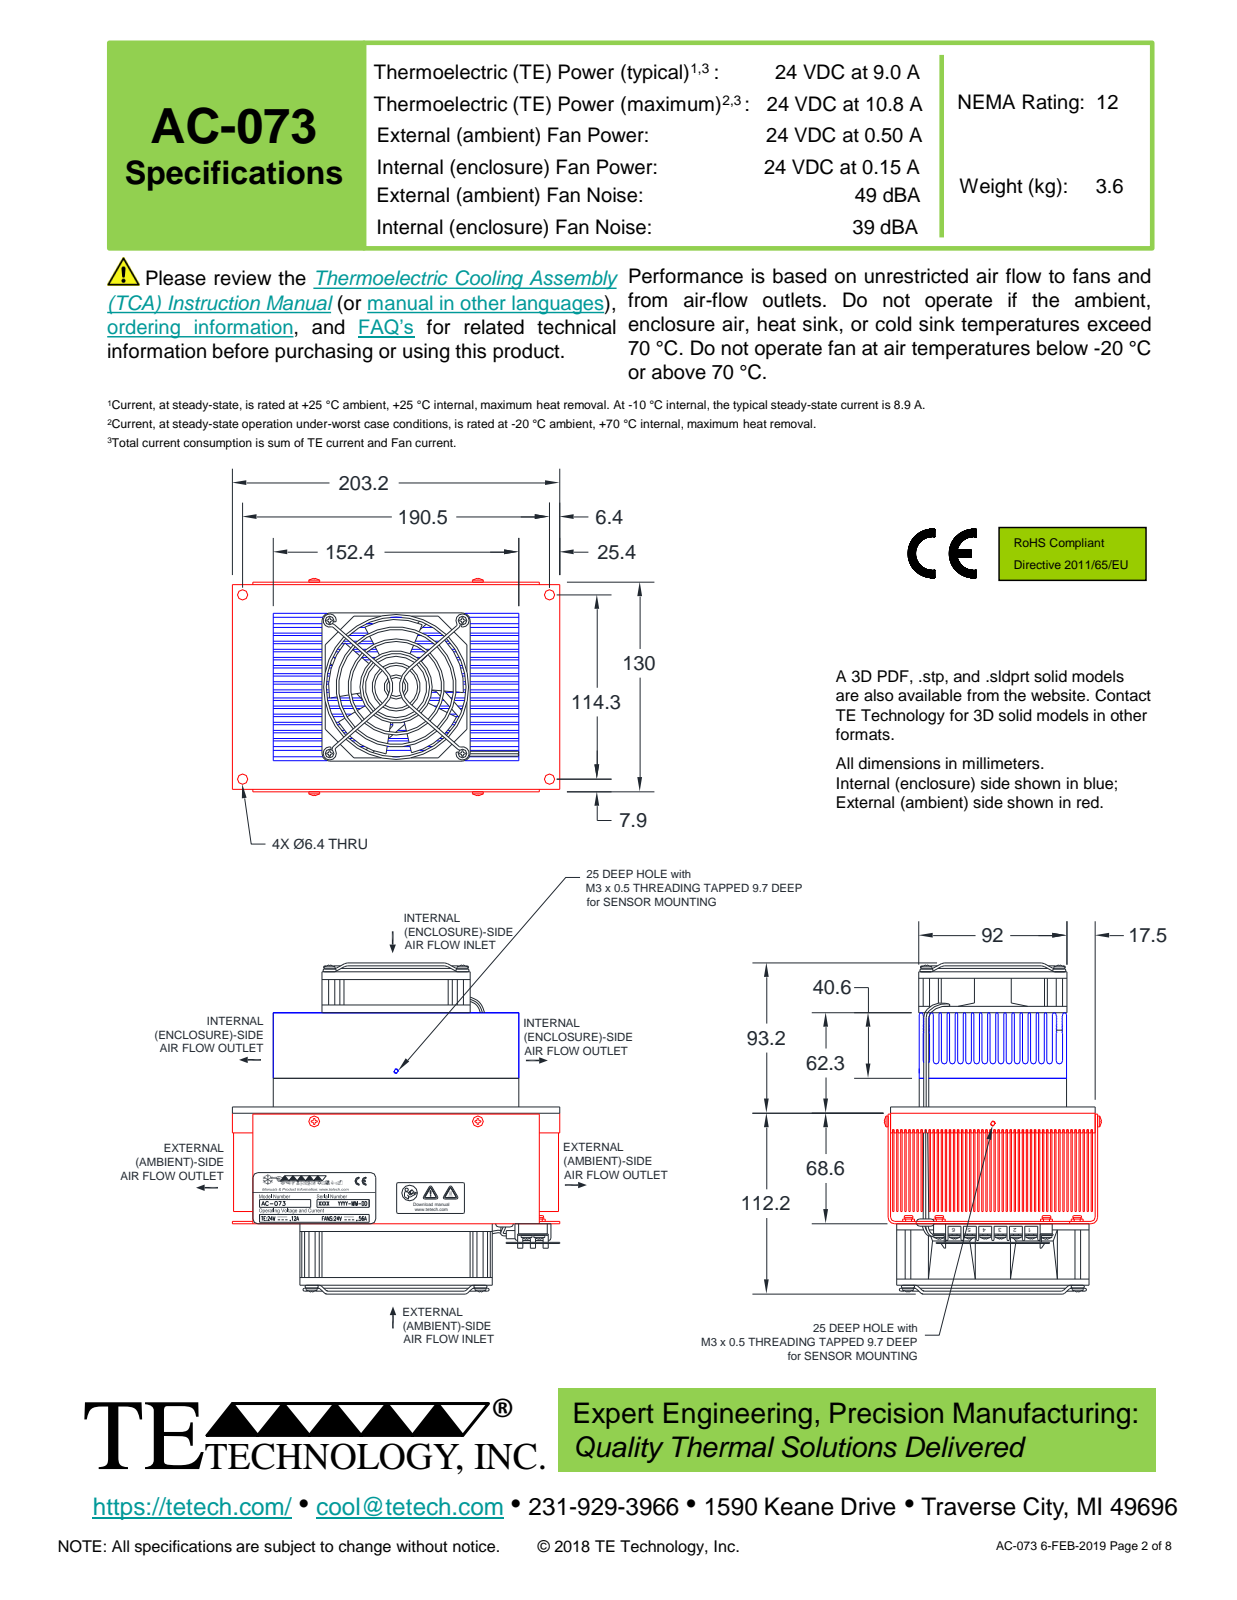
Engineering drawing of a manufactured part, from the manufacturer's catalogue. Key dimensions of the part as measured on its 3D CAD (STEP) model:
Part name (STEP PRODUCT): 825-4658-001 heat sink assy; 3111 G heat sink shroud; PEM LKS 6-32-2; 3111-G shroud with PEMS (+8 more)
STEP written by: Alibre (AUTOMOTIVE_DESIGN)
Units: millimetres
Bodies: 159 solids, 4938 faces (2260 planar, 1048 cylindrical, 1630 other)
Overall size (bounding box): 205.53 × 203.34 × 135.08
Volume: 1 605 000 mm³ · Surface area: 1 512 000 mm²
Round holes (diameter × count): ⌀2.64 ×18, ⌀2.65 ×8, ⌀4.22 ×8, ⌀5.56 ×8, ⌀6.35 ×8, ⌀1.91 ×6, ⌀3.53 ×6, ⌀3.94 ×6, ⌀4.32 ×6, ⌀4.83 ×5, ⌀4.17 ×4, ⌀4.27 ×4
Round bosses / shafts (diameter × count): ⌀1.42 ×32, ⌀3.51 ×26, ⌀1.8 ×19, ⌀6.86 ×18, ⌀6.34 ×8, ⌀5.74 ×8, ⌀1.65 ×7, ⌀4.9 ×6
Partial cylindrical surfaces — rounded edges, fillets, slot ends (radius × count): R1 ×100, R0.5 ×83, R0.3 ×27, R0.79 ×24, R0.76 ×22, R0.95 ×21, R0.2 ×18, R1.75 ×15
Main face-to-face distances: 5.03, 2.51, 10.06, 1.7, 7.54, 3.33, 2.52, 1.6, 29.36, 7.55
Hole centre spacings: 7.87, 19.05, 20.61, 9.52, 9.53, 12.35, 12.36, 18.98
